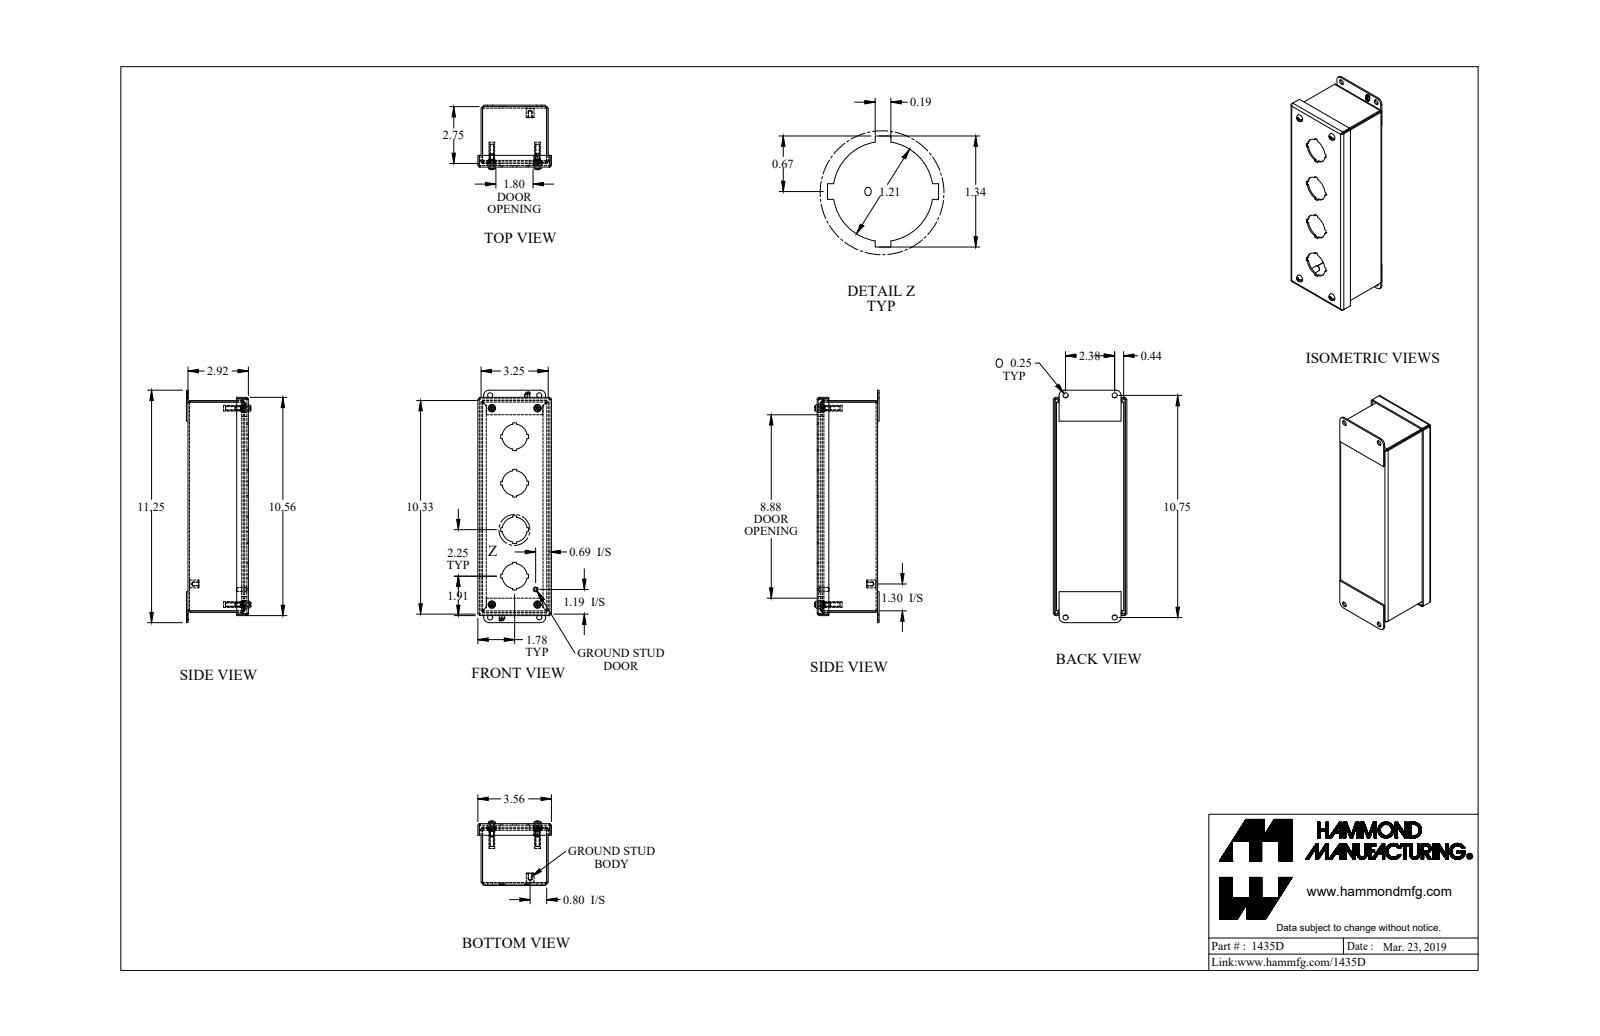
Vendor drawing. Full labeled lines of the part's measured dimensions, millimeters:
Part name (STEP PRODUCT): 1435D_Default
STEP written by: SolidWorks 2019 (CONFIG_CONTROL_DESIGN)
Units: millimetres
Bodies: 19 solids, 619 faces (407 planar, 156 cylindrical, 56 other)
Overall size (bounding box): 285.8 × 90.5 × 79.3
Volume: 240 100 mm³ · Surface area: 246 300 mm²
Round holes (diameter × count): ⌀6.4 ×8, ⌀4 ×4, ⌀10.3 ×4, ⌀30.7 ×4, ⌀4 ×1
Round bosses / shafts (diameter × count): ⌀9.9 ×4, ⌀7 ×4, ⌀4.8 ×4, ⌀3.8 ×4, ⌀9.5 ×1, ⌀6.4 ×1, ⌀4.8 ×1
Partial cylindrical surfaces — rounded edges, fillets, slot ends (radius × count): R0.9 ×12, R2.7 ×12, R4.1 ×4, R4.3 ×4, R6.4 ×4
Main face-to-face distances: 1.8, 72.4, 1.8, 80.7, 74.2, 70.6, 82.6, 78.9, 258.5, 4
Hole centre spacings: 241.3, 257.2, 263.7, 247.8, 60.4, 16, 16, 44.8
